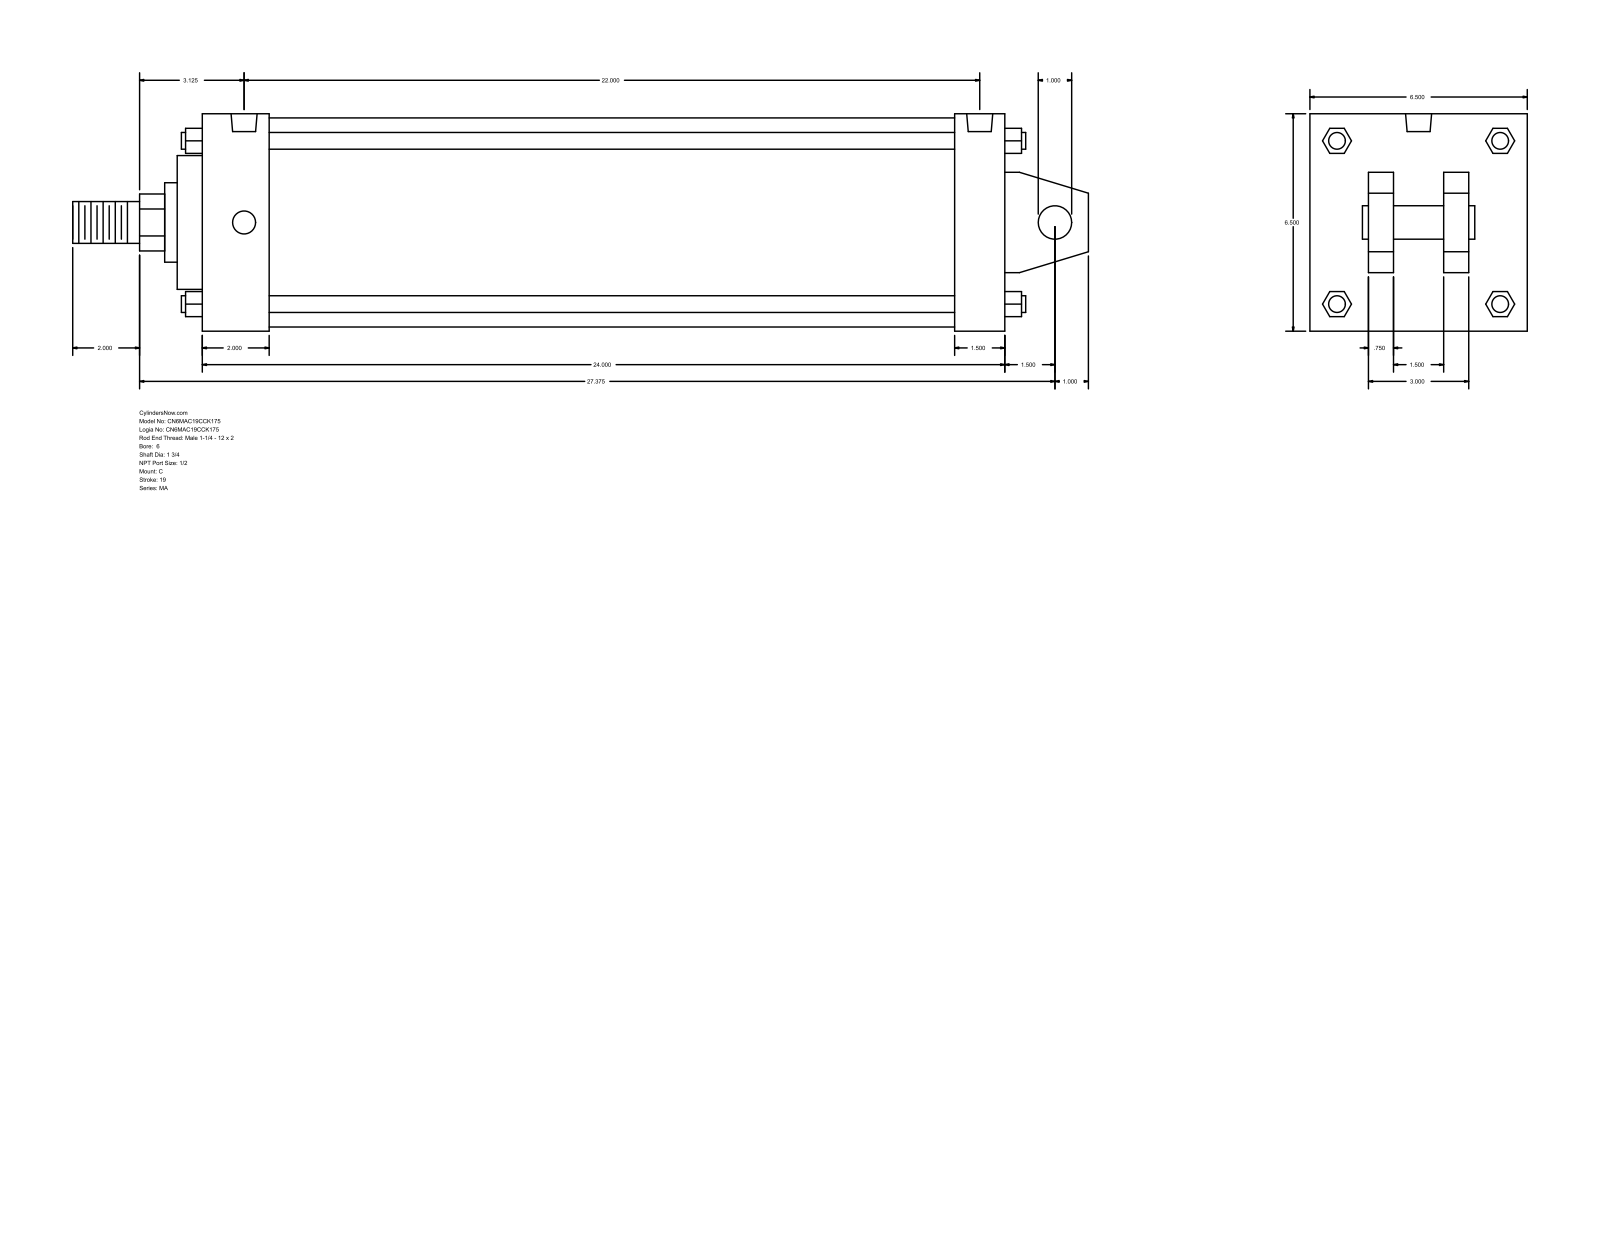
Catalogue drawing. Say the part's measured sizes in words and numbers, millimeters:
The part is named "MA_C__0600_1.75". Its 3-D file was written by "GSSL Pune (CONFIG_CONTROL_DESIGN)". It is 0 solids with 141 faces: 109 planar, 32 cylindrical and 0 other. Overall it measures 771.52 by 165.1 by 165.1 millimeters. Round holes: 4 of diameter 17.46, 2 of diameter 19.77. Round bosses or shafts: 4 of diameter 12.7, 1 of diameter 158.75, 1 of diameter 101.6, 1 of diameter 60.33, 1 of diameter 44.45, 1 of diameter 31.75, 1 of diameter 25.4. Partial cylindrical surfaces (rounded edges, fillets, slot ends): 1 of radius 21.63. The main face-to-face distances are 165.1, 609.61, 19.05, 63.5, 101.6, 50.8, 44.45, 120.65, 571.5, 57.15. The hole center spacings are 558.79.
